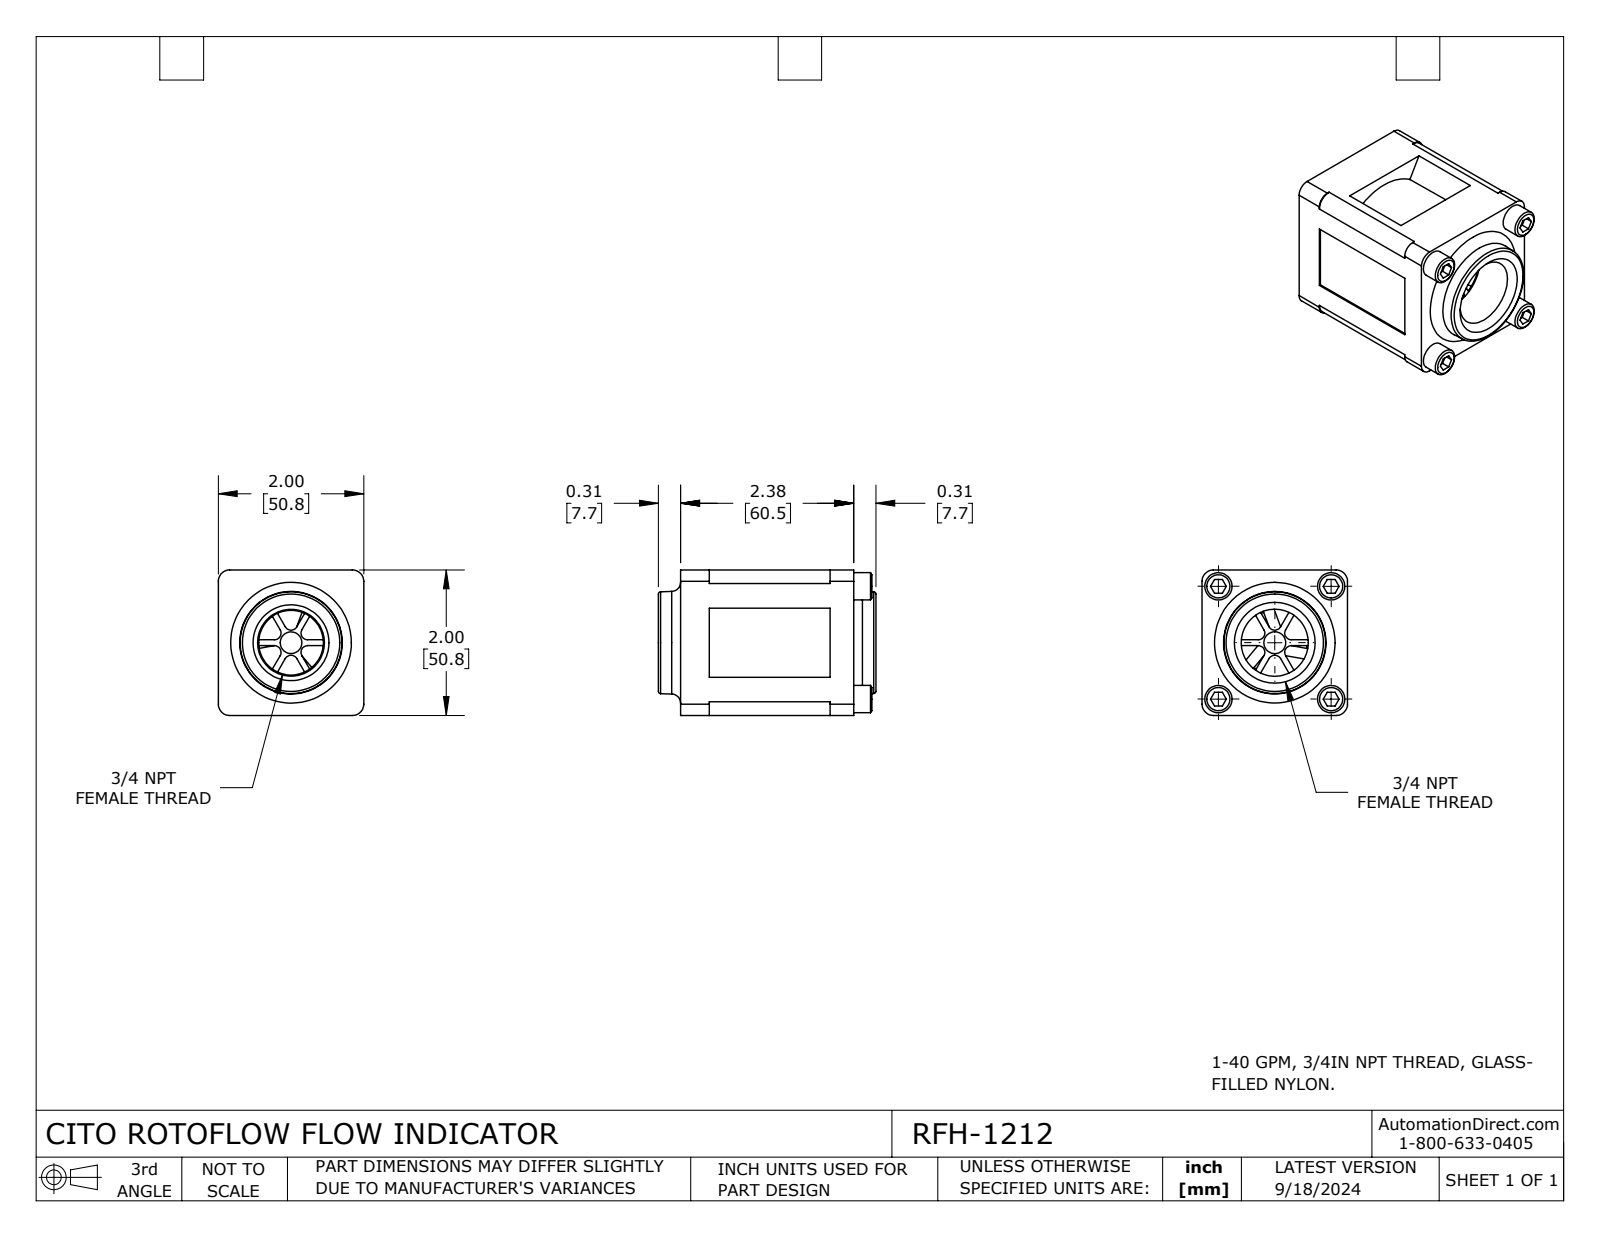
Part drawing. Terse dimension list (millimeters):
name: RFH-1212
written by: SolidWorks 2023 (CONFIG_CONTROL_DESIGN)
unit: mm
bodies: 4 solids, 366 faces (135 planar, 167 cylindrical, 64 other)
size: 75.9 × 50.8 × 50.8
volume: 107 800 mm³; area: 53 780 mm²
holes: 4× ⌀5.1, 4× ⌀6.5, 1× ⌀3.1, 1× ⌀4.7, 1× ⌀7.6, 1× ⌀23.4
bosses: 4× ⌀9.5, 1× ⌀36.8, 1× ⌀3.2
rounds: 18× R2.3, 6× R1.2, 4× R4, 4× R4.7, 1× R16.1, 1× R17.6
face distances: 50.8, 0.5, 50.3, 50.4, 10, 7.7, 17.8, 2, 60.5, 49.8
hole spacings: 27.8, 39.4, 55.7
